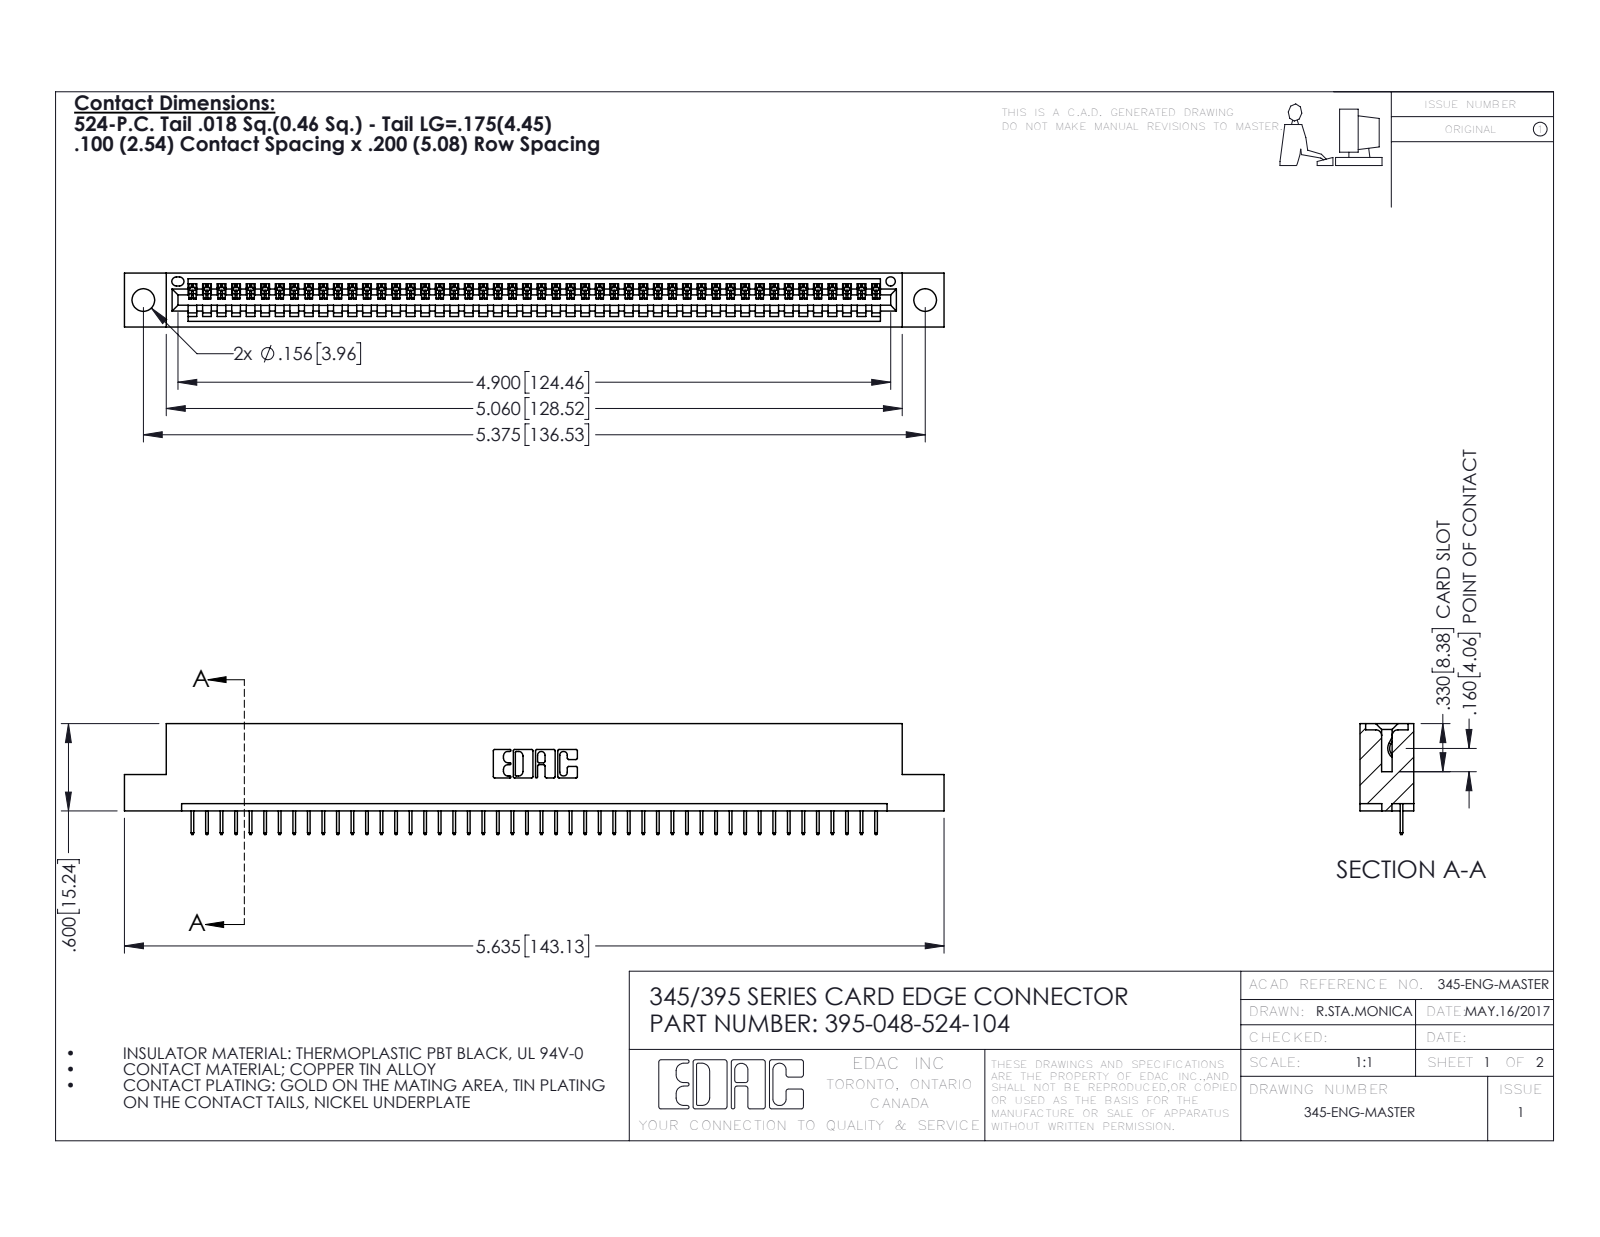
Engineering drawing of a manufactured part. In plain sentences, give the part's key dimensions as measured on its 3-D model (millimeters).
The part is named "345 Part_Flush Mounting Lugs - 0.156 Dia-TH; 395-048-524-104; 345-292-001_345-293-124". Its 3-D file was written by "SolidWorks 2016 (CONFIG_CONTROL_DESIGN)". It is 49 solids with 3102 faces: 2288 planar, 814 cylindrical and 0 other. Overall it measures 143.1 by 19.4 by 9.4 millimeters. Its volume is 13 400 cubic millimeters and its surface area 17 050 square millimeters. Round holes: 2 of diameter 4, 1 of diameter 1.6. Partial cylindrical surfaces (rounded edges, fillets, slot ends): 96 of radius 0.2, 22 of radius 0.3, 6 of radius 0.2, 6 of radius 0.8, 3 of radius 0.7, 2 of radius 0.8, 2 of radius 1, 1 of radius 0.4. The main face-to-face distances are 7.6, 1.8, 9.4, 5.1, 2.5, 6.9, 0.6, 5.7, 1.8, 3.8. The hole center spacings are 6.9, 130.5, 136.5.
